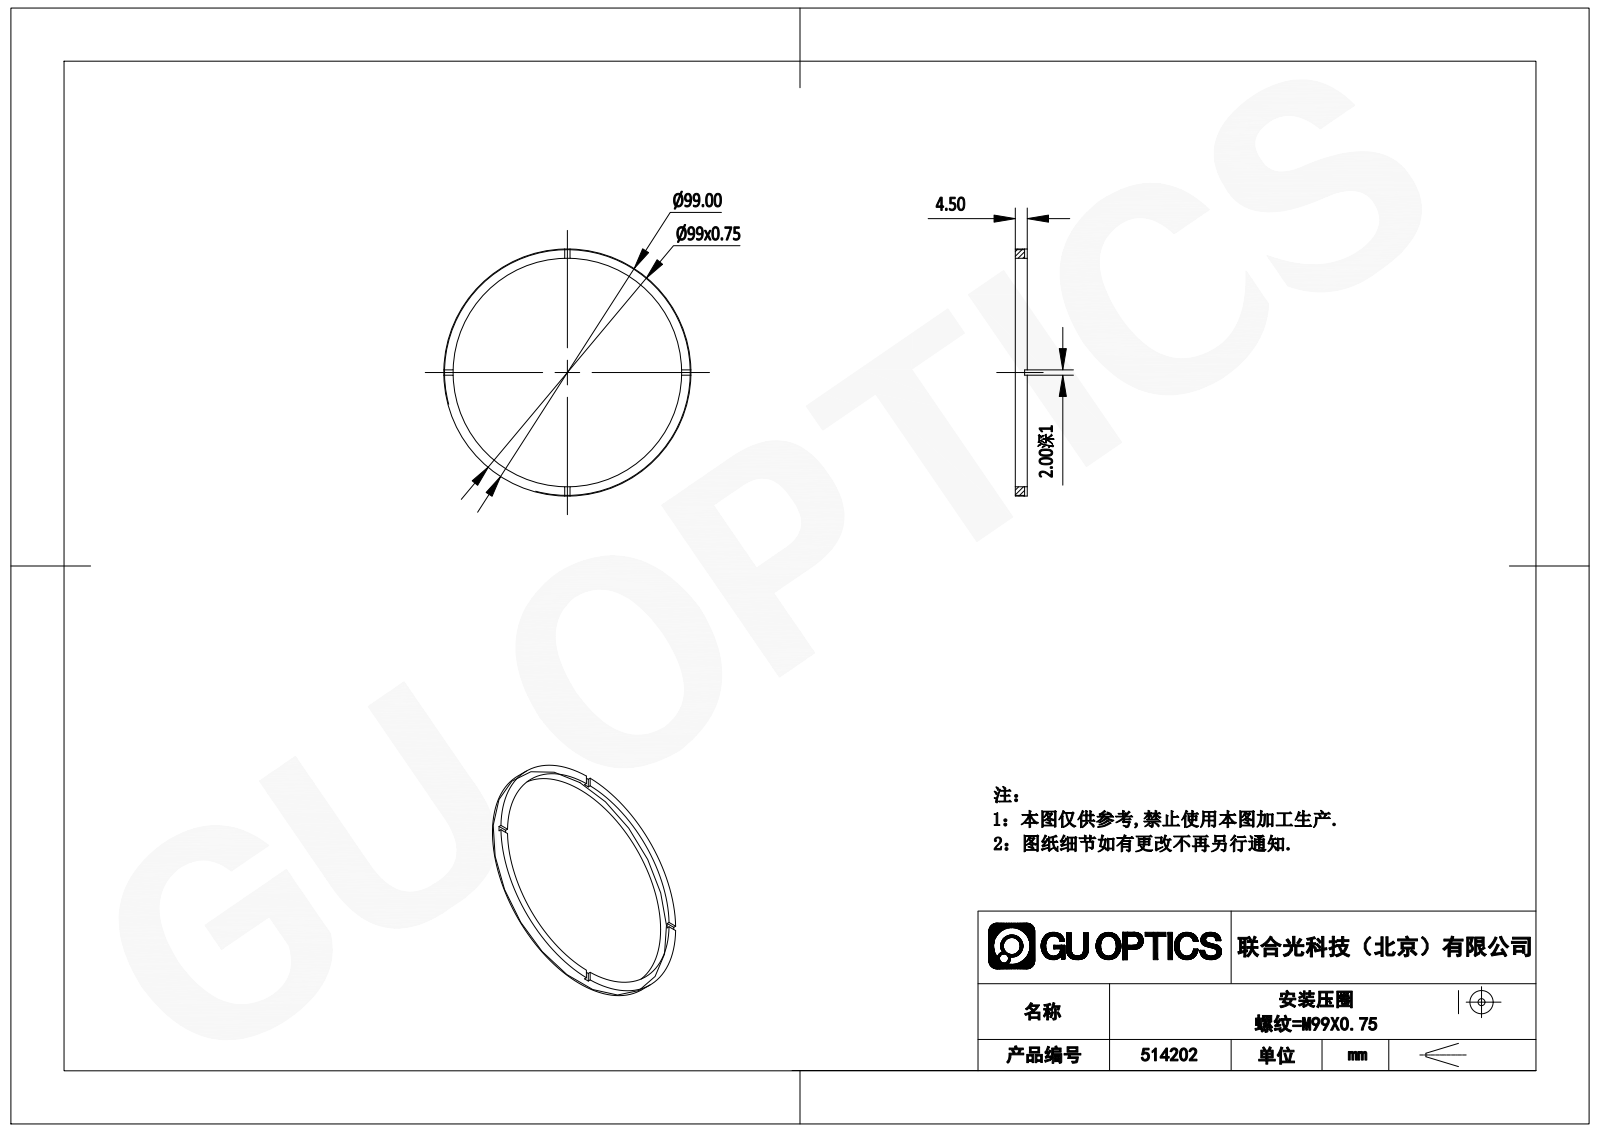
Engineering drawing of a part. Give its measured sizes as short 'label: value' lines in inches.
name: 514202
written by: SolidWorks 2020 (CONFIG_CONTROL_DESIGN)
unit: in
bodies: 1 solid, 21 faces (17 planar, 4 cylindrical, 0 other)
size: 3.898 × 3.898 × 0.177
volume: 0.287 in³; area: 7.459 in²
holes: 1× ⌀3.622
bosses: 1× ⌀3.898
face distances: 0.177, 0.138, 0.039, 0.079
